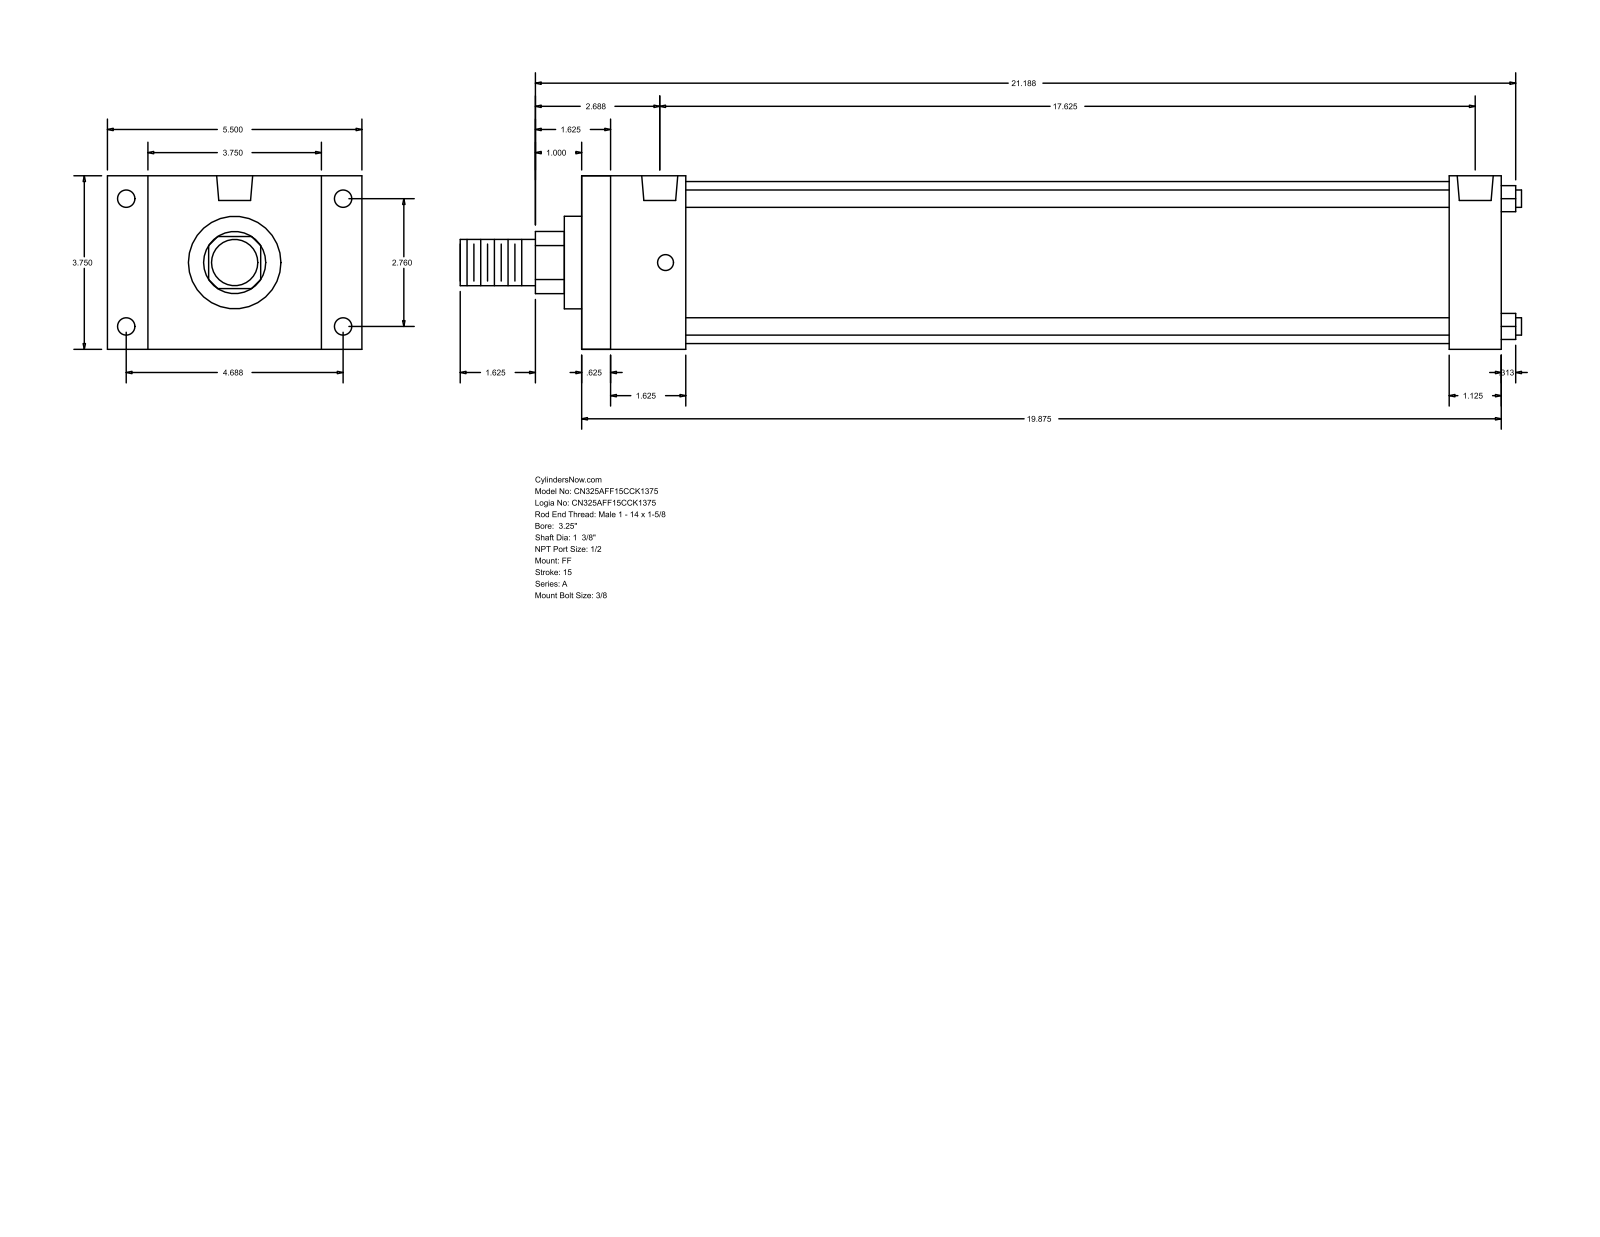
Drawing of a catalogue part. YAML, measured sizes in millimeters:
part_name: "A_FF__0325_1.375"
step_written_by: "GSSL Pune (CONFIG_CONTROL_DESIGN)"
units: millimeters
bodies: {solids: 0, faces: 92, planar: 64, cylindrical: 28, other: 0}
overall_size: [582.61, 139.7, 95.25]
round_holes:
  - {diameter: 8.73, count: 4}
  - {diameter: 9.53, count: 4}
  - {diameter: 19.77, count: 2}
round_bosses_or_shafts:
  - {diameter: 9.53, count: 4}
  - {diameter: 88.9, count: 1}
  - {diameter: 50.8, count: 1}
  - {diameter: 34.92, count: 1}
  - {diameter: 25.4, count: 1}
partial_cylinders:
  - {radius: 17.06, count: 1}
face_to_face_distances: [95.24, 504.83, 15.87, 488.96, 57.15, 28.58, 22.23, 117.47, 476.25, 41.28]
hole_center_spacings: [3.18, 70.1, 119.06, 138.16, 441.32, 444.5, 447.68]
